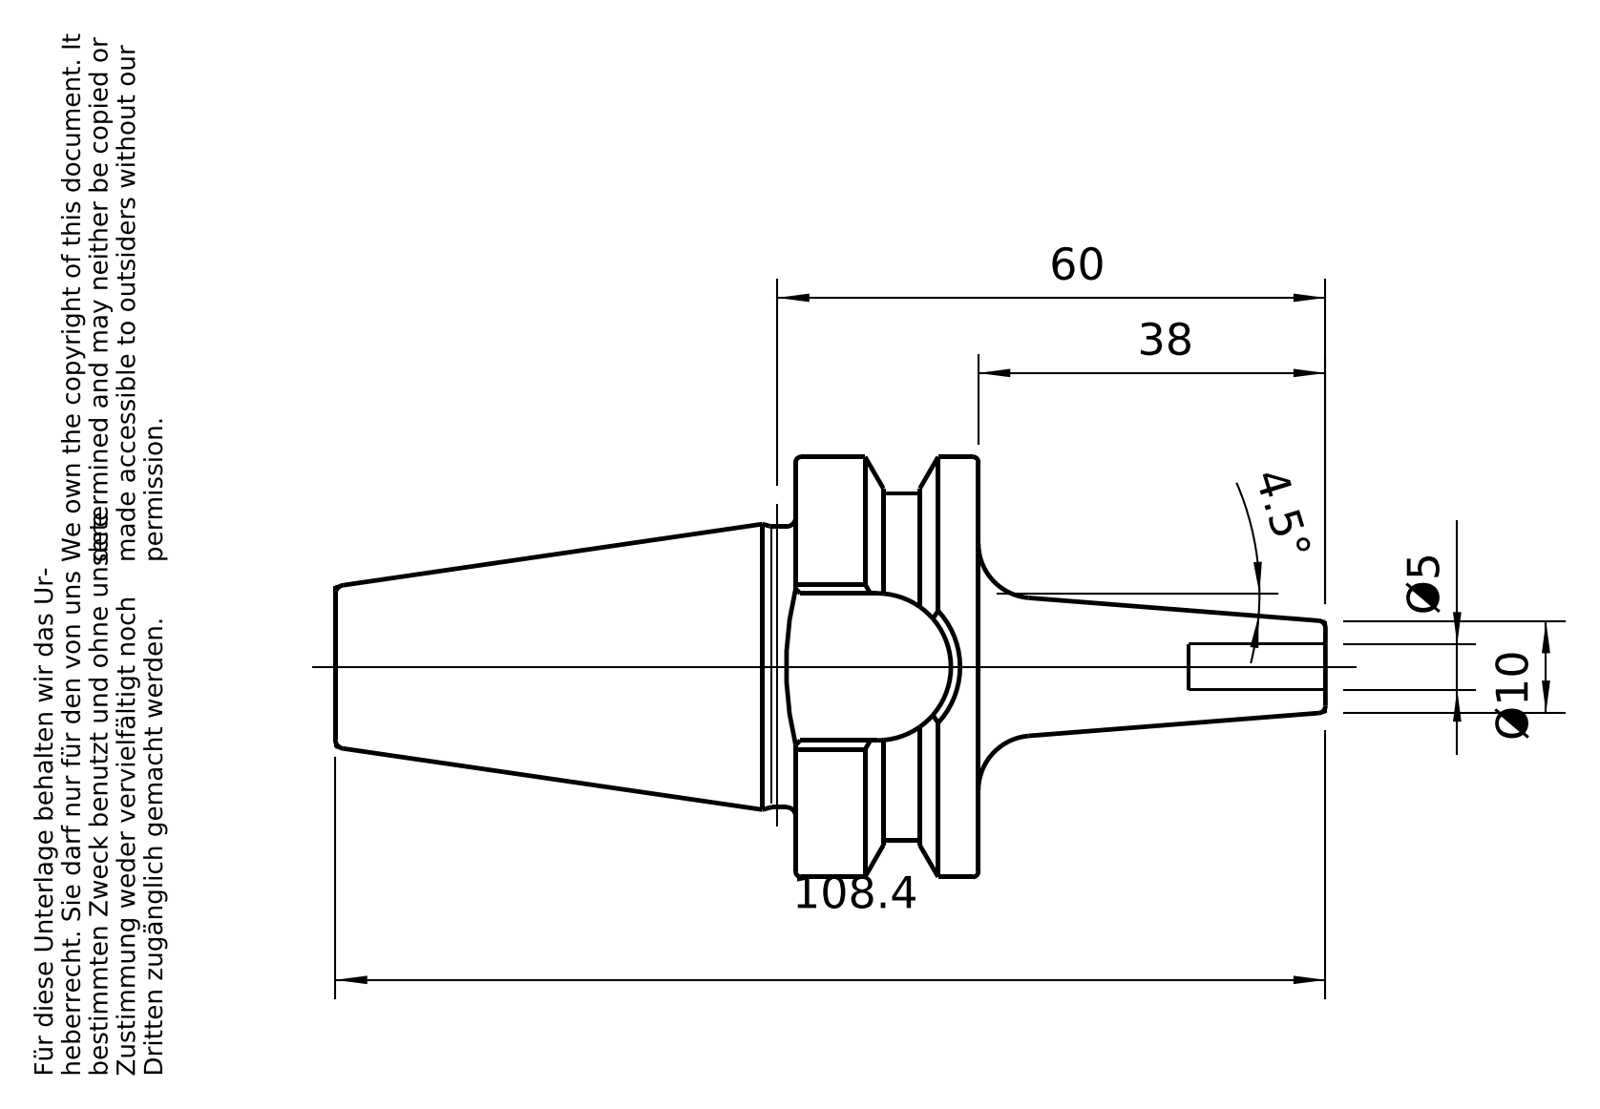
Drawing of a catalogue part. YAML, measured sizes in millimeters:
part_name: "30-645-05"
step_written_by: "PRO/ENGINEER BY PARAMETRIC TECHNOLOGY CORPORATION, 2010430 (CONFIG_CONTROL_DESIGN)"
units: millimeters
bodies: {solids: 1, faces: 94, planar: 26, cylindrical: 20, other: 48}
overall_size: [108.4, 45.98, 45.98]
volume: 54717
surface_area: 13411
round_holes:
  - {diameter: 5, count: 1}
  - {diameter: 10.11, count: 1}
  - {diameter: 12.51, count: 1}
  - {diameter: 13, count: 1}
round_bosses_or_shafts:
  - {diameter: 45.98, count: 1}
  - {diameter: 30.75, count: 1}
  - {diameter: 12.01, count: 1}
partial_cylinders:
  - {radius: 8.1, count: 1}
  - {radius: 18.88, count: 1}
face_to_face_distances: [20, 32.3, 16.2, 50.4, 70.4, 108.4, 58, 38, 25, 25.4]
